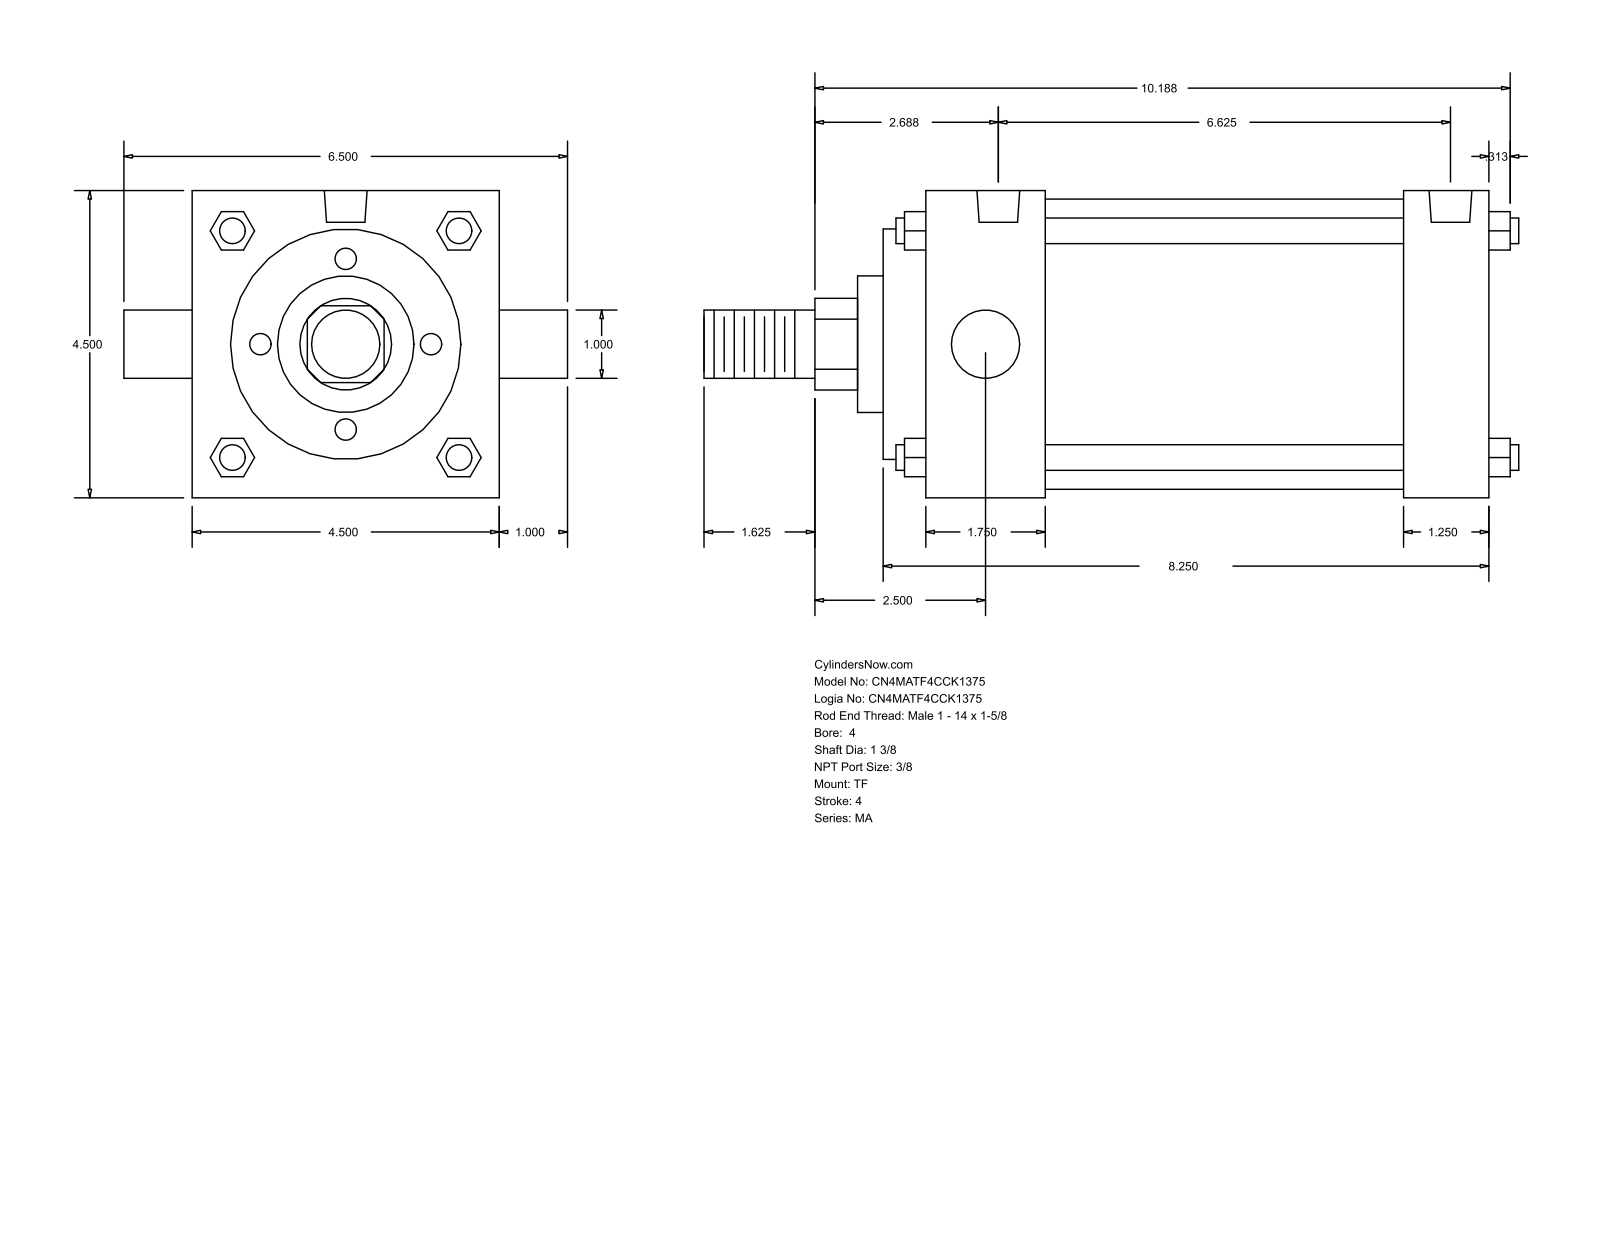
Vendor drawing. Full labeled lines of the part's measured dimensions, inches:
Part name (STEP PRODUCT): MA_TF__0400_1.375
STEP written by: GSSL Pune (CONFIG_CONTROL_DESIGN)
Units: inches
Bodies: 0 solids, 122 faces (93 planar, 29 cylindrical, 0 other)
Overall size (bounding box): 11.937 × 6.5 × 4.5
Round holes (diameter × count): ⌀0.437 ×3, ⌀0.627 ×2
Round bosses / shafts (diameter × count): ⌀0.375 ×4, ⌀1 ×2, ⌀4.25 ×1, ⌀3.375 ×1, ⌀2 ×1, ⌀1.375 ×1
Partial cylindrical surfaces — rounded edges, fillets, slot ends (radius × count): R0.672 ×1
Main face-to-face distances: 4.5, 8.25, 8.875, 6.5, 0.625, 7.625, 7, 1.25, 2.375, 1.75
Hole centre spacings: 0.187, 0.188, 6.25, 6.437, 6.438, 6.625
